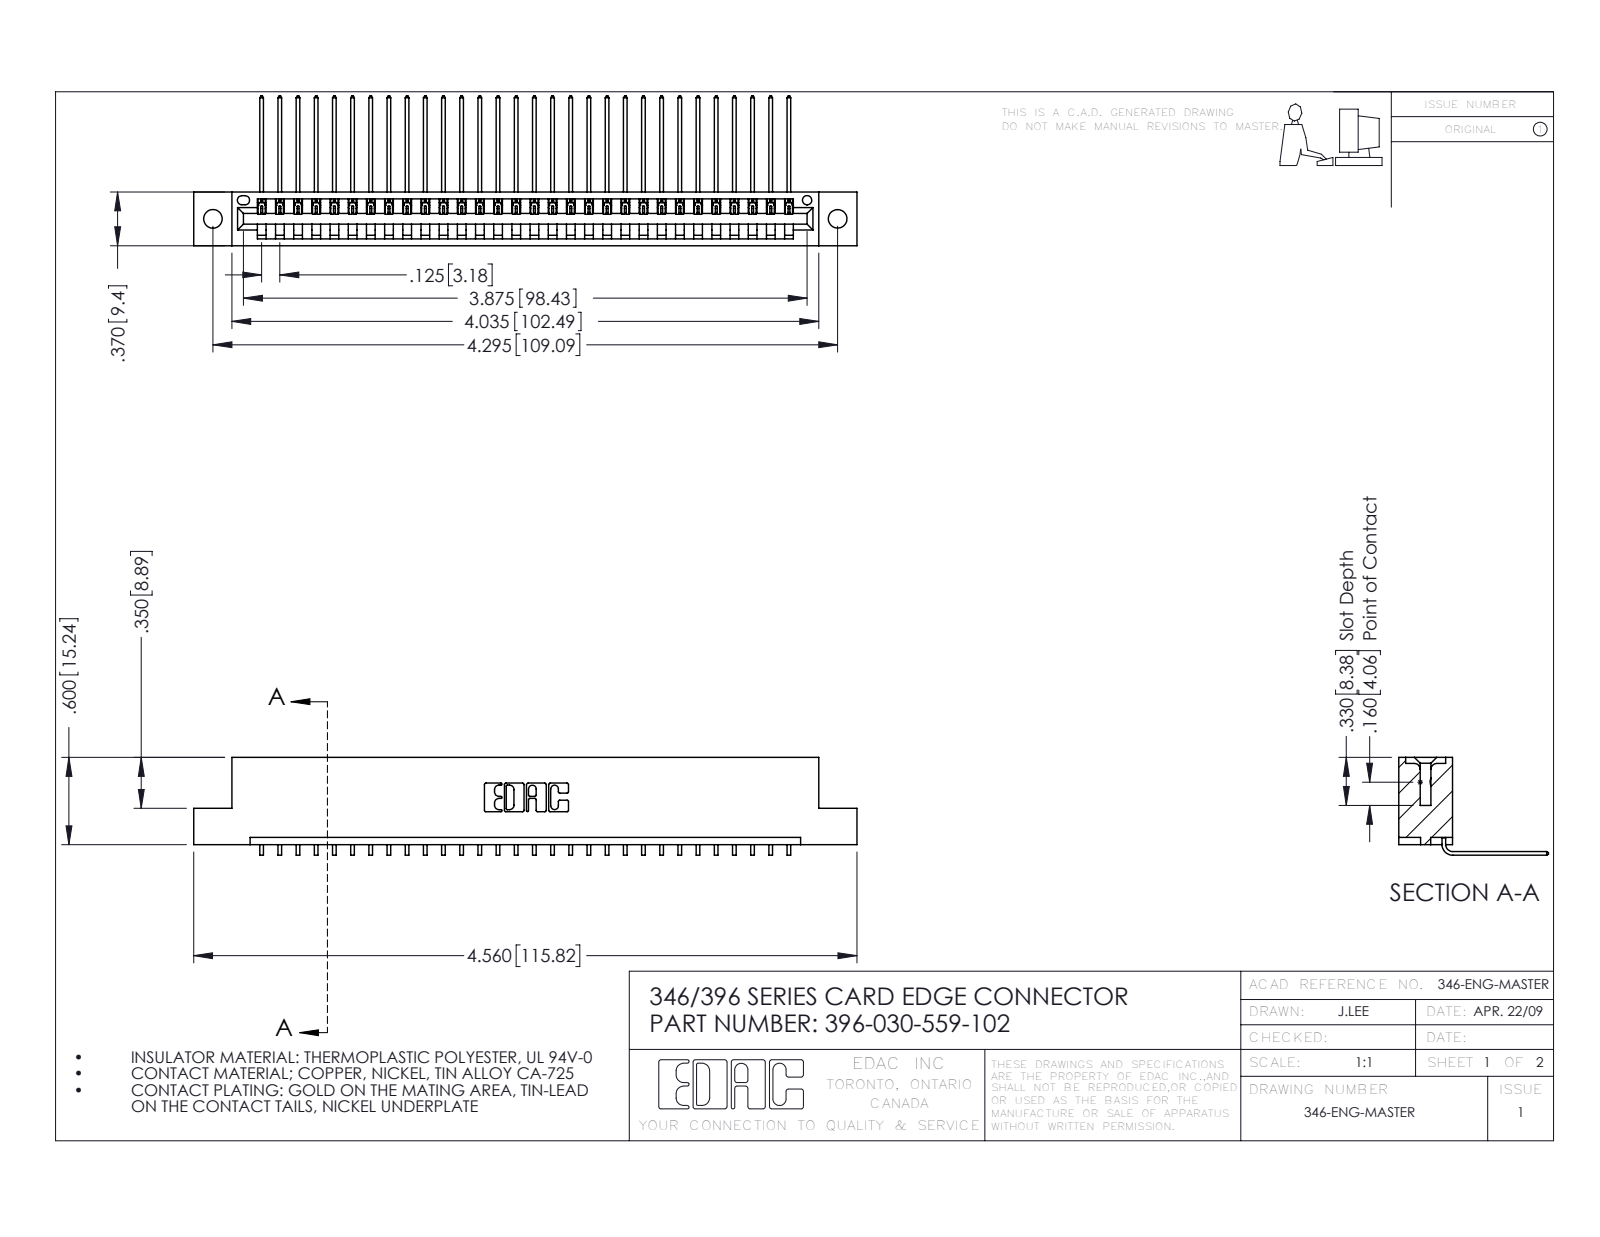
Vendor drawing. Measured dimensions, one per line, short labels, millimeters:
name: 345-292-001_558 559 Tail - 1; 346 Part_Flush Mounting Lugs - 0.128 Dia; 396-030-559-102
written by: SolidWorks 2016 (CONFIG_CONTROL_DESIGN)
unit: mm
bodies: 31 solids, 1922 faces (1336 planar, 586 cylindrical, 0 other)
size: 115.8 × 26.2 × 17.1
volume: 11 100 mm³; area: 14 030 mm²
holes: 2× ⌀3.3, 1× ⌀1.6
rounds: 60× R0.2, 22× R0.3, 6× R0.2, 6× R0.8, 3× R0.7, 2× R0.8, 2× R1, 1× R0.4
face distances: 1.2, 8.2, 9.4, 6.4, 1.8, 0.6, 7.6, 3.8, 5.6, 2.5
hole spacings: 6.2, 103.8, 109.1
